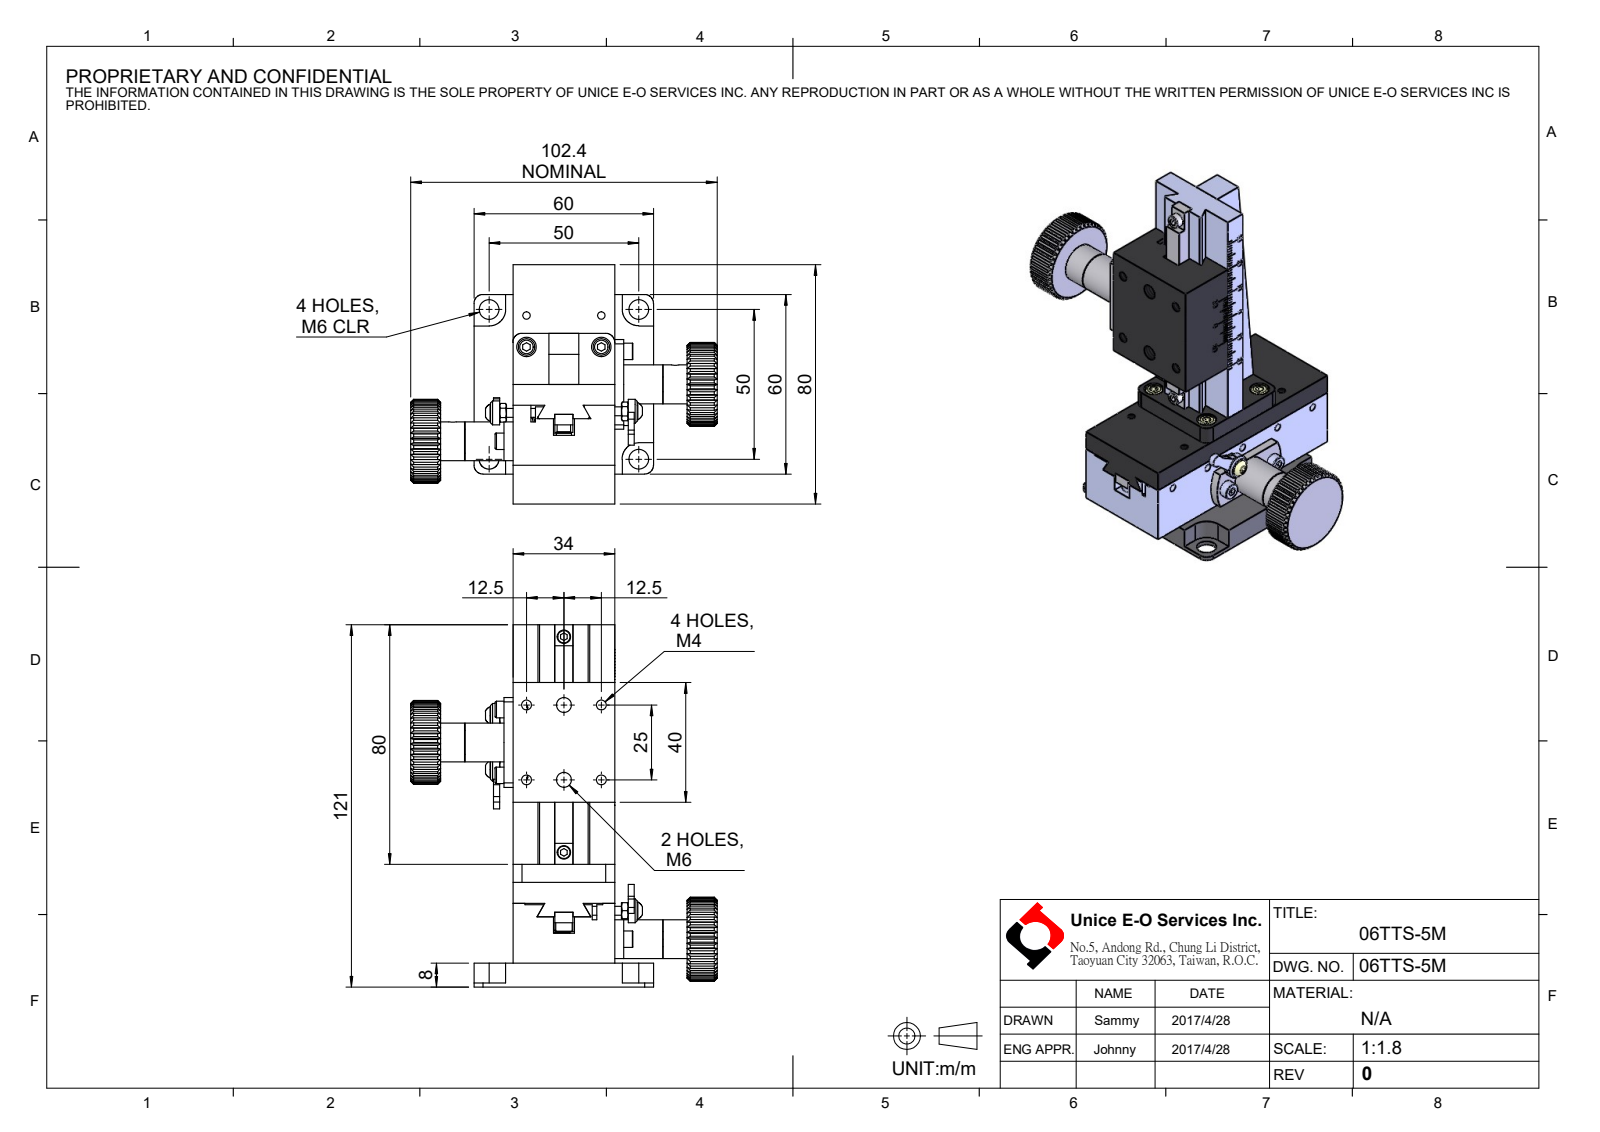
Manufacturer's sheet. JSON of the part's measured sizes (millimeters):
{"part_name": "06TTS-5M", "step_written_by": "SolidWorks 2016 (CONFIG_CONTROL_DESIGN)", "units": "millimeters", "bodies": {"solids": 51, "faces": 3336, "planar": 1941, "cylindrical": 677, "other": 718}, "overall_size": [121, 102.4, 80], "volume_mm3": 179521, "surface_area_mm2": 79937, "round_holes": [[2.5, 31], [3.4, 12], [6.5, 12], [2.05, 8], [3.3, 8], [5, 5], [2.9, 4], [3, 4], [4, 4], [5.5, 4], [6.6, 4], [3.5, 3]], "round_bosses_or_shafts": [[3, 17], [5.5, 16], [8, 5], [5.7, 3], [13, 2], [4.5, 2], [4, 2], [2.5, 2]], "partial_cylinders_radius": [[4, 12], [3, 8], [5.5, 4], [2, 3], [2.25, 3], [0.5, 2], [14, 2], [15, 2]], "face_to_face_distances": [10, 7, 20, 27, 8, 6, 4.5, 13, 35, 34], "hole_center_spacings": [27.95, 12.5, 25, 17.68, 35.36, 39.53, 45.07, 37.5]}
